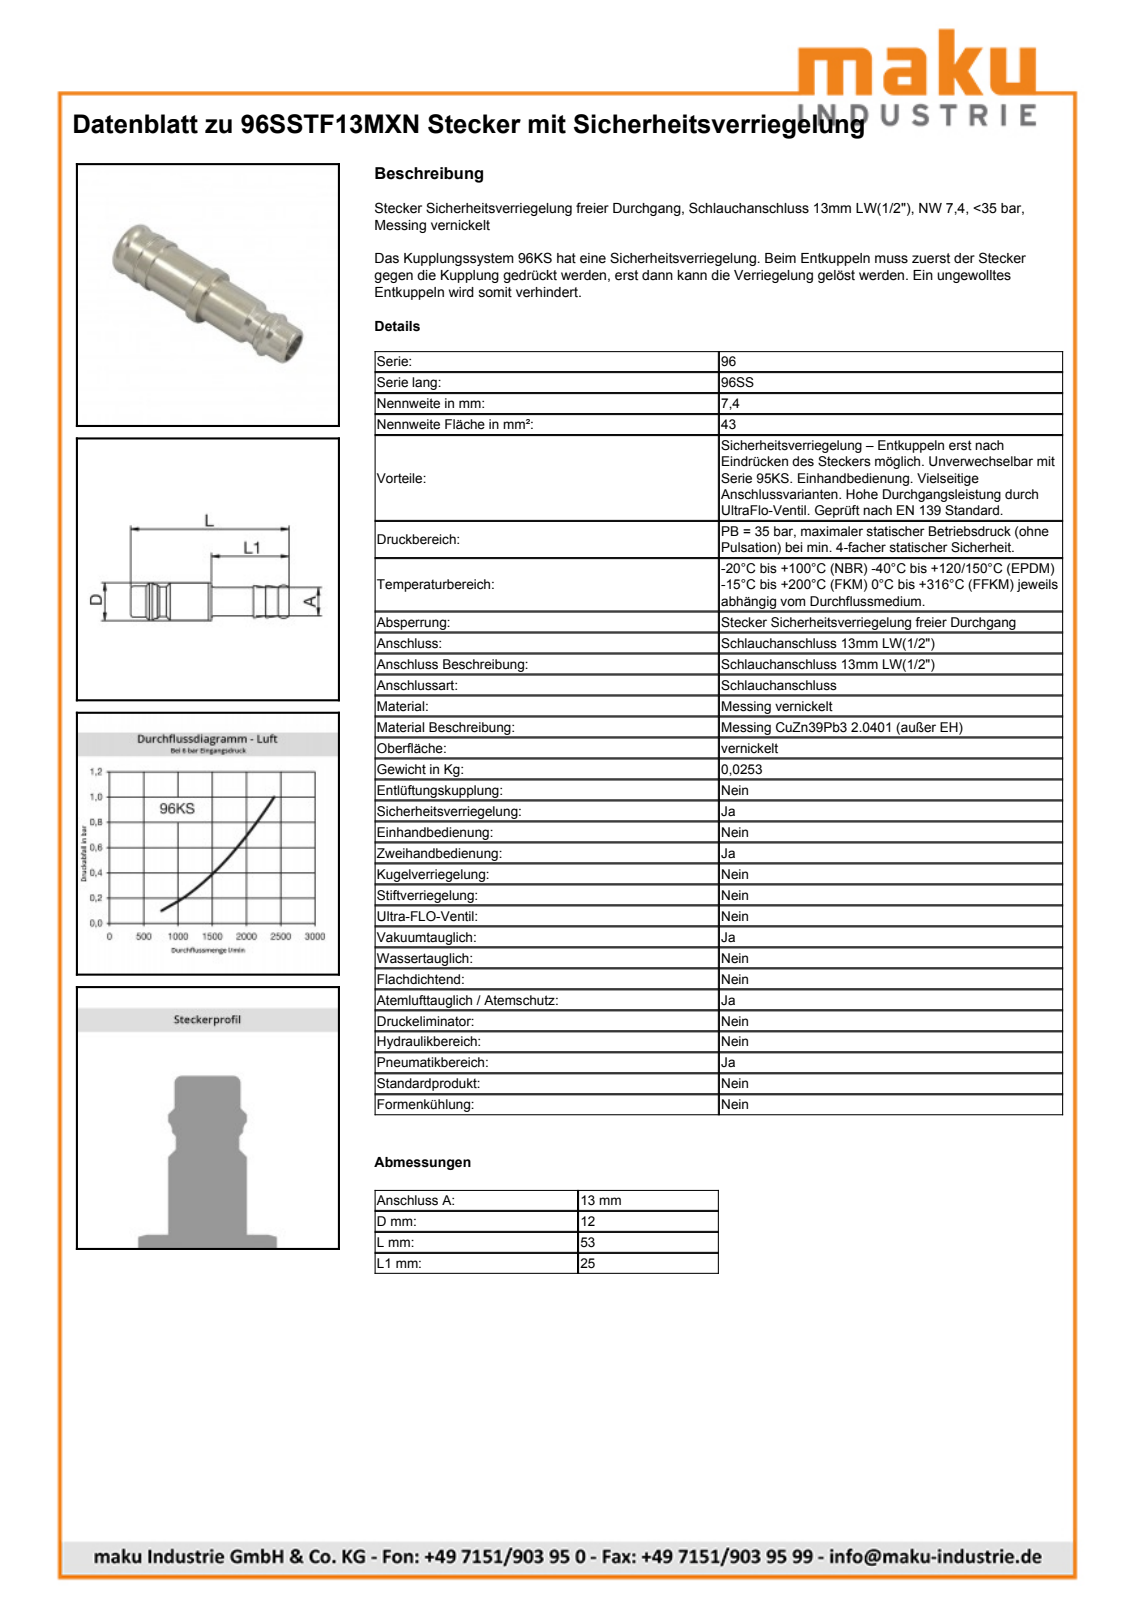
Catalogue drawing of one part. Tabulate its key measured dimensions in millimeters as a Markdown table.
| quantity | value |
| --- | --- |
| part name | D102879 |
| STEP written by | Autodesk Inventor 2011 (AUTOMOTIVE_DESIGN) |
| units | millimeters |
| bodies | 1 solid, 29 faces (5 planar, 9 cylindrical, 15 other) |
| overall size | 53 × 15 × 15 |
| volume | 2 961 mm³ |
| surface area | 3 858 mm² |
| round holes (diameter × count) | 7.4 × 1, 11 × 1 |
| round bosses / shafts (diameter × count) | 15 × 1, 13.1 × 1, 11.95 × 1, 10.8 × 1, 9.9 × 1, 9.6 × 1 |
| main face-to-face distances | 2.9, 27.9, 25, 25.1, 28, 53, 41.5, 16.4, 13.5, 11.5 |
